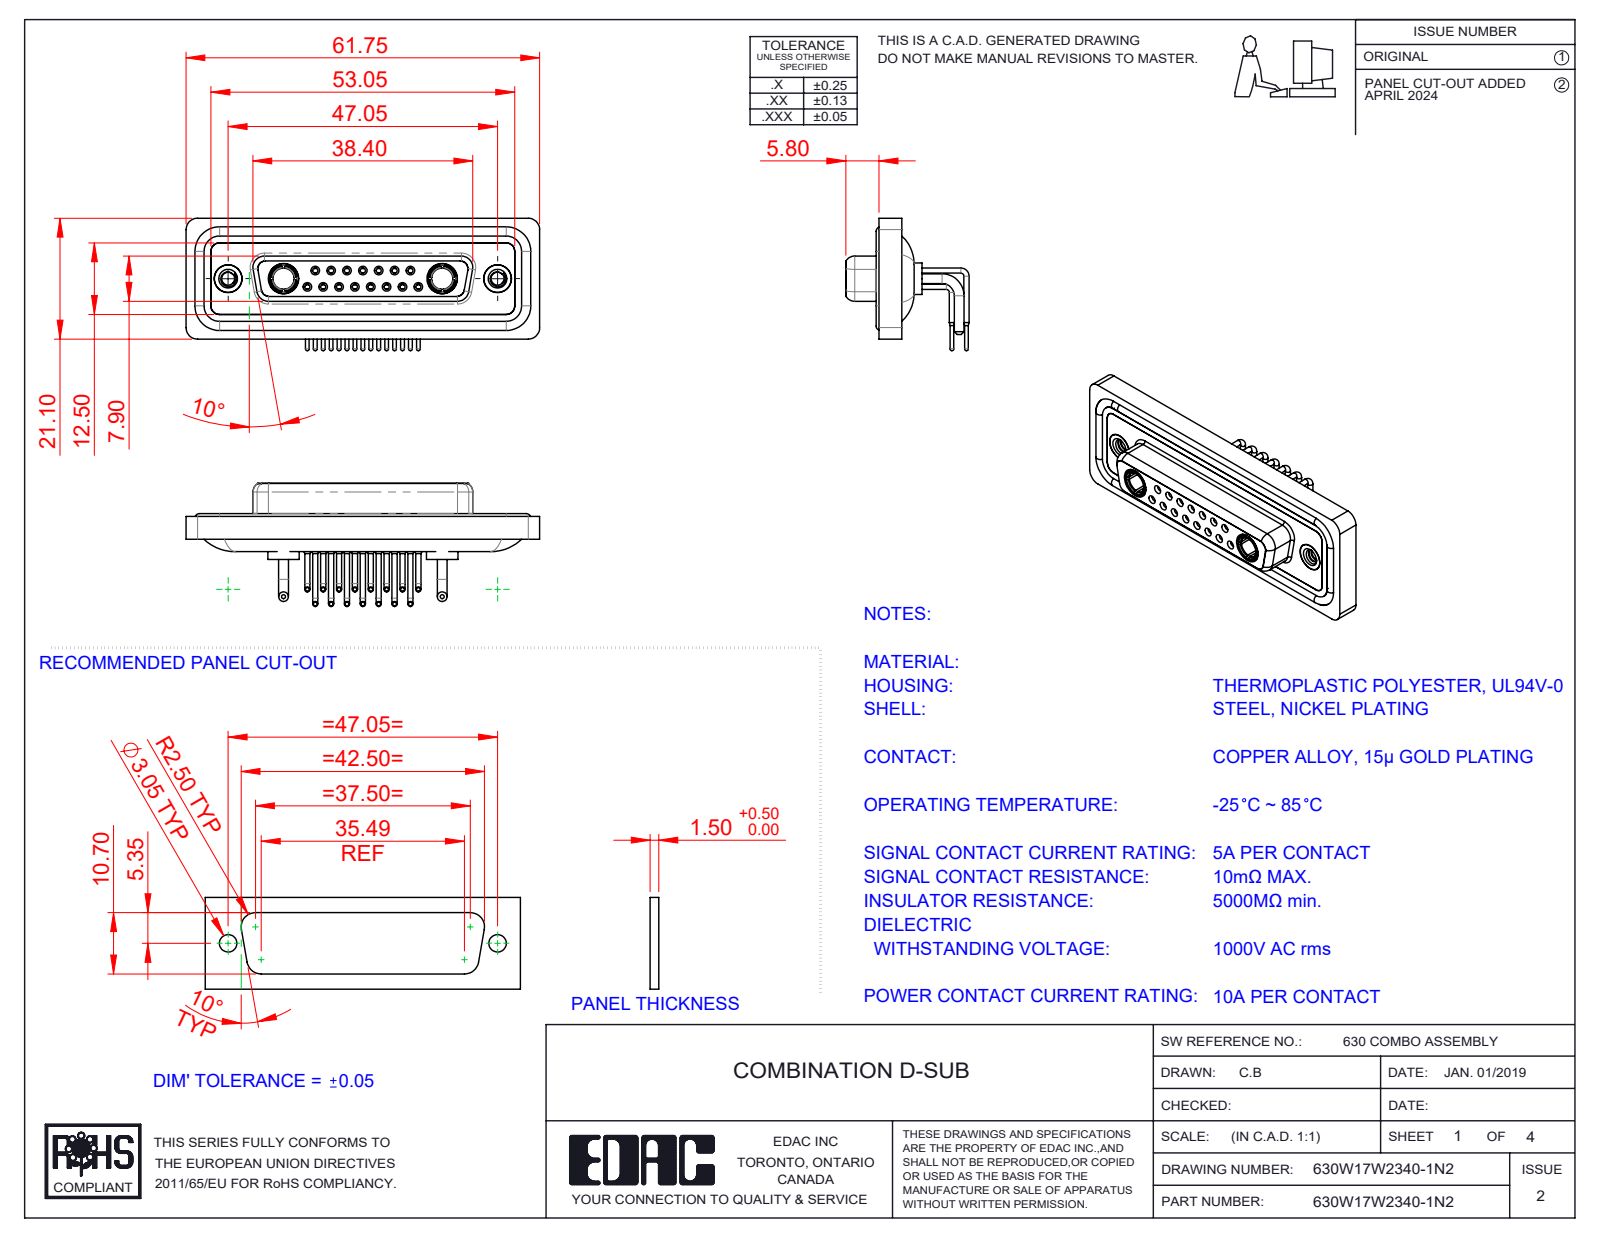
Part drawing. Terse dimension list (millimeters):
name: 630Combo Contact Row 1_50 Contacts; 630Combo Threaded Rivet_2; 630Combo Housing_17W2; 630Combo Waterproof Housing_25 Contacts (+5 more)
written by: SolidWorks 2023 (CONFIG_CONTROL_DESIGN)
unit: mm
bodies: 26 solids, 1337 faces (388 planar, 583 cylindrical, 366 other)
size: 61.75 × 23.12 × 21.53
volume: 8 371 mm³; area: 14 429 mm²
holes: 15× ⌀0.9, 15× ⌀1.1, 15× ⌀1.5, 15× ⌀2, 8× ⌀1.6, 7× ⌀1.7, 4× ⌀4.85, 2× ⌀2.26, 2× ⌀3.7, 2× ⌀4, 2× ⌀4.05, 2× ⌀5
bosses: 15× ⌀0.9, 15× ⌀0.65, 11× ⌀1.6, 4× ⌀1.7, 2× ⌀5.5, 2× ⌀5.2, 2× ⌀4.96, 2× ⌀4.95
rounds: 18× R1.5, 18× R2, 8× R1.35, 8× R1.6, 4× R0.25, 4× R0.5, 4× R0.6, 4× R0.65
face distances: 0.4, 1.8, 4.1, 1.1, 1.6, 1.5, 3.1, 2.5, 3.7, 1.4
hole spacings: 3.16, 2.77, 5.54, 8.31, 5.04, 7.49, 11.08, 5.03
